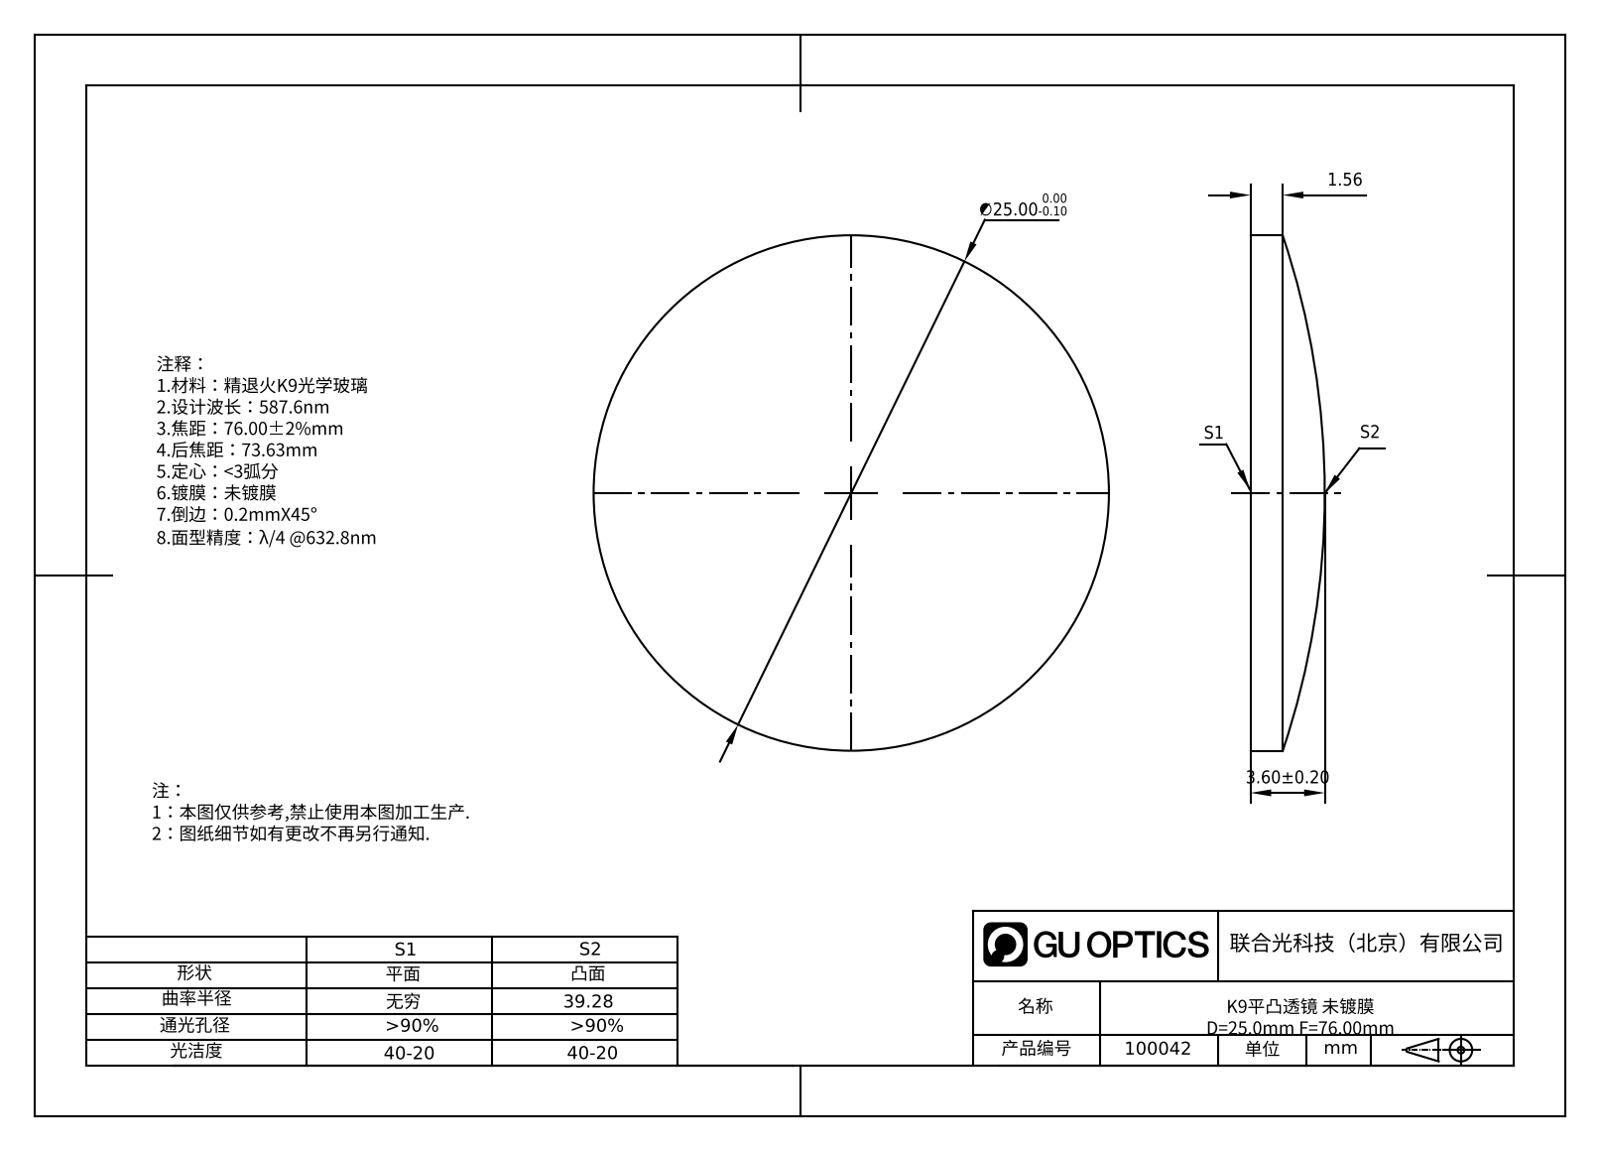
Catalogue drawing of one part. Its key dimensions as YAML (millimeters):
part_name: "100042"
step_written_by: "SolidWorks 2016 (AUTOMOTIVE_DESIGN)"
units: millimeters
bodies: {solids: 1, faces: 5, planar: 1, cylindrical: 2, other: 2}
overall_size: [25, 25, 3.6]
volume: 1271
surface_area: 1117
round_bosses_or_shafts:
  - {diameter: 25, count: 1}
